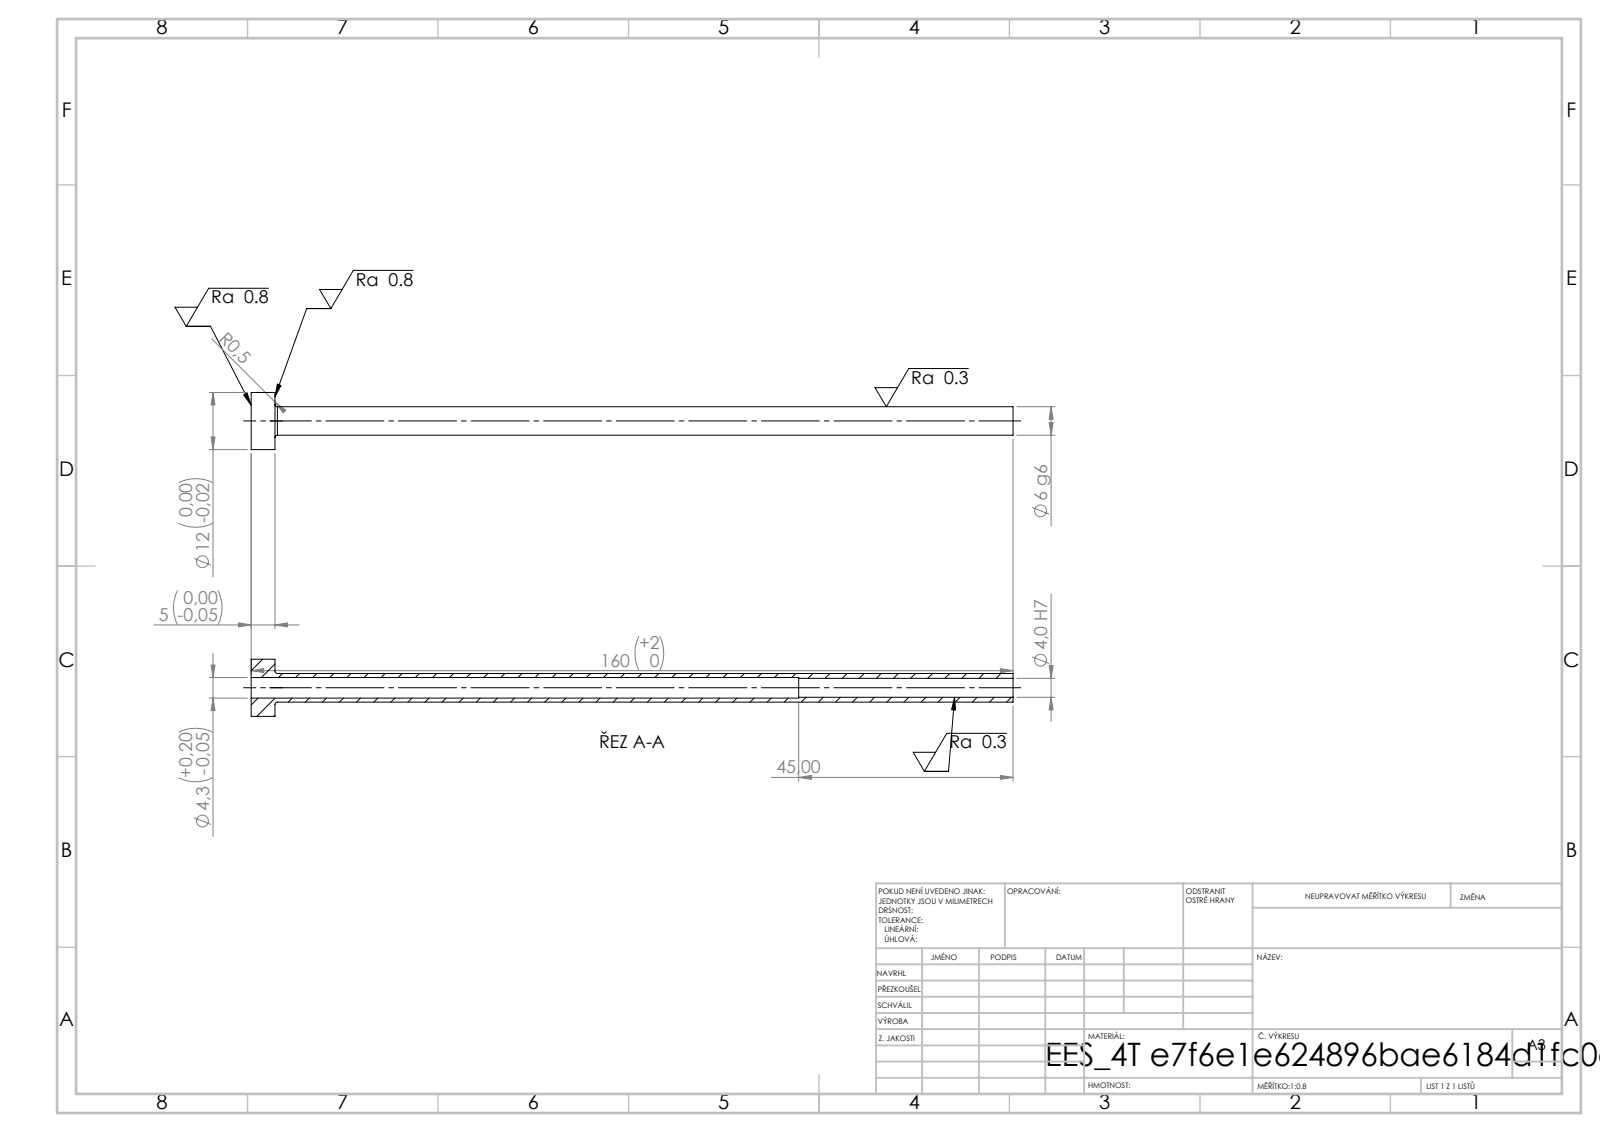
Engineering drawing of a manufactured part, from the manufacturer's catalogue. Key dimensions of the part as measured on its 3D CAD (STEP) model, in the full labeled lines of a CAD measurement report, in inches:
STEP written by: SolidWorks 2019 (CONFIG_CONTROL_DESIGN)
Units: inches
Bodies: 1 solid, 14 faces (4 planar, 8 cylindrical, 2 other)
Overall size (bounding box): 6.299 × 0.472 × 0.472
Volume: 0.166 in³ · Surface area: 8.41 in²
Round holes (diameter × count): ⌀0.157 ×1, ⌀0.169 ×1
Round bosses / shafts (diameter × count): ⌀0.472 ×1, ⌀0.236 ×1
Main face-to-face distances: 0.197, 6.299, 6.102, 4.528, 4.331, 1.772
